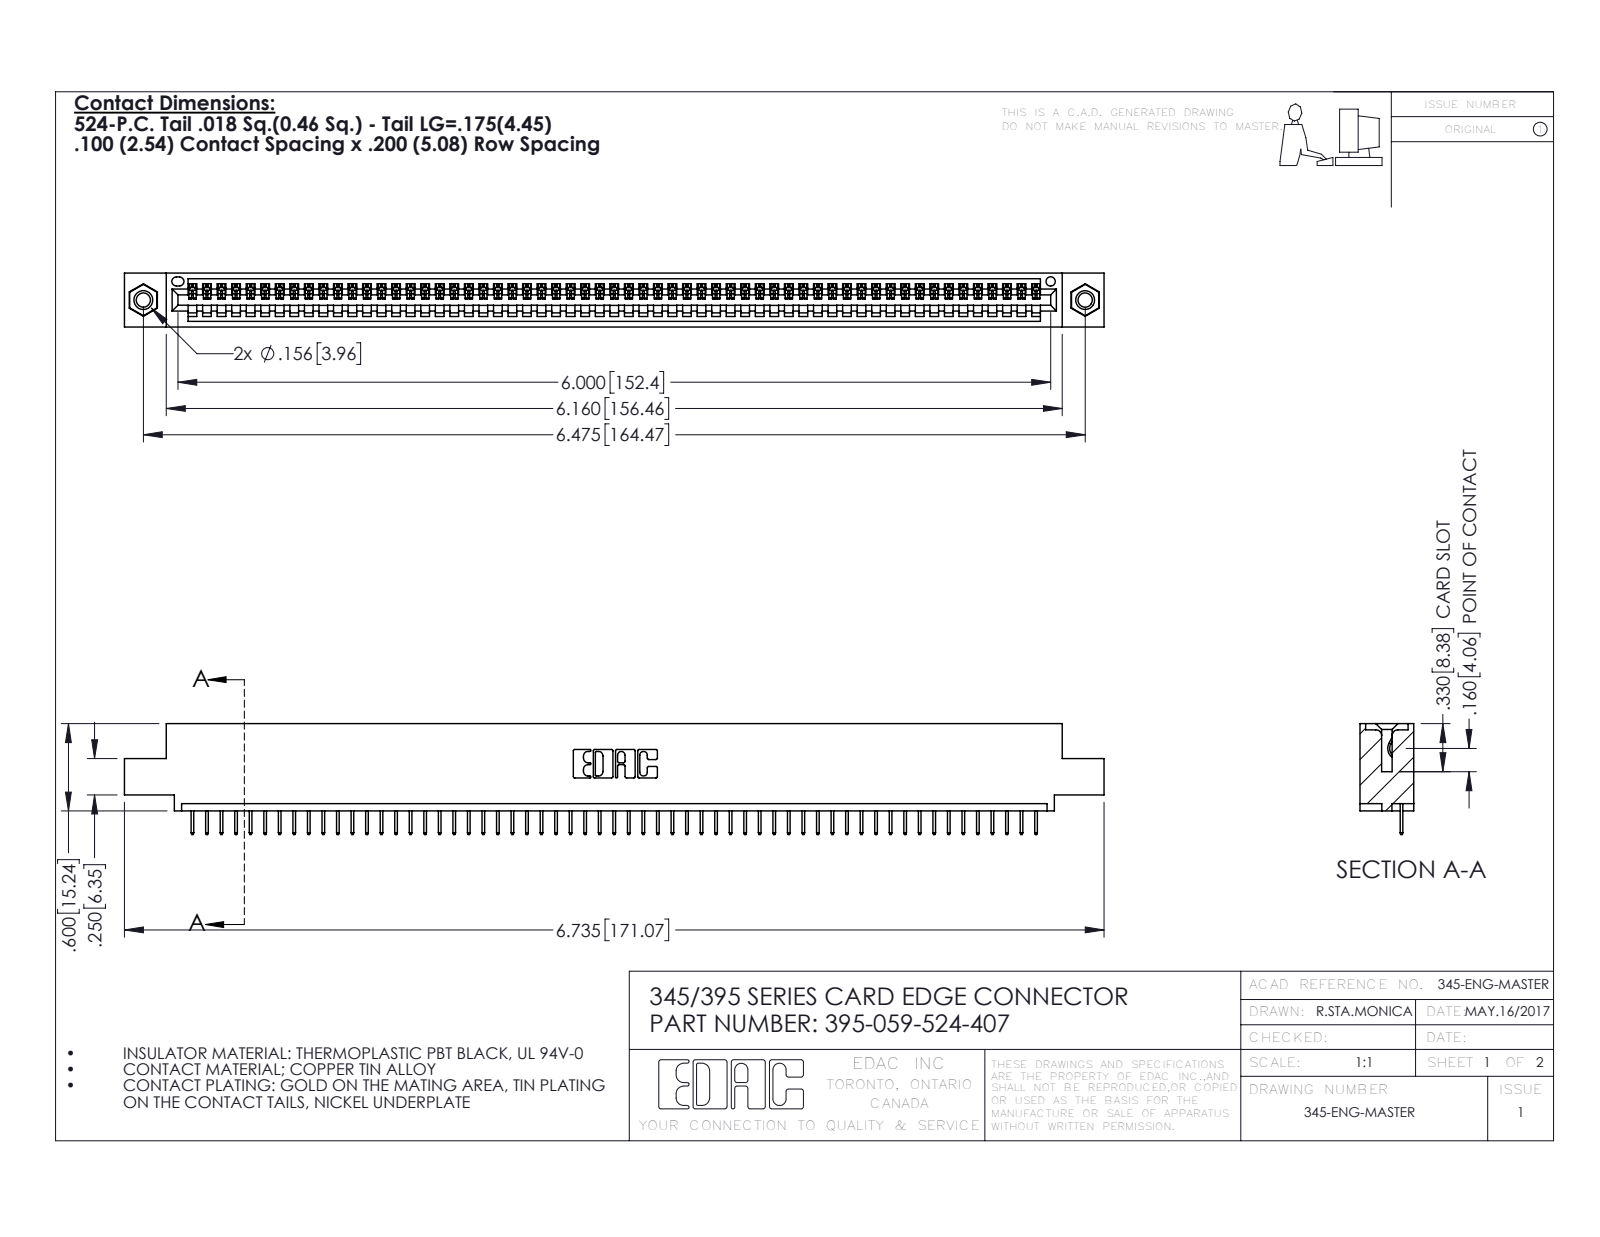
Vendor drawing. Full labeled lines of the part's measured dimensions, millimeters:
Part name (STEP PRODUCT): 345 Part_0.110 Offset - 0.156 Dia-TI; 395-059-524-407; 345-250-001_345-250-005-103; 345-292-001_345-293-124
STEP written by: SolidWorks 2016 (CONFIG_CONTROL_DESIGN)
Units: millimetres
Bodies: 62 solids, 3848 faces (2830 planar, 1002 cylindrical, 16 other)
Overall size (bounding box): 171.1 × 19.4 × 9.4
Volume: 16 100 mm³ · Surface area: 20 950 mm²
Round holes (diameter × count): ⌀2.5 ×2, ⌀3.2 ×2, ⌀4 ×2, ⌀1.6 ×1
Round bosses / shafts (diameter × count): ⌀3.9 ×2
Partial cylindrical surfaces — rounded edges, fillets, slot ends (radius × count): R0.2 ×118, R0.3 ×22, R0.2 ×6, R0.8 ×6, R0.7 ×3, R0.8 ×2, R1 ×2, R0.4 ×1
Main face-to-face distances: 1.8, 7.6, 9.4, 5.1, 2.5, 6.9, 0.6, 5.7, 1.8, 3.8
Hole centre spacings: 6.9, 158.5, 164.5
